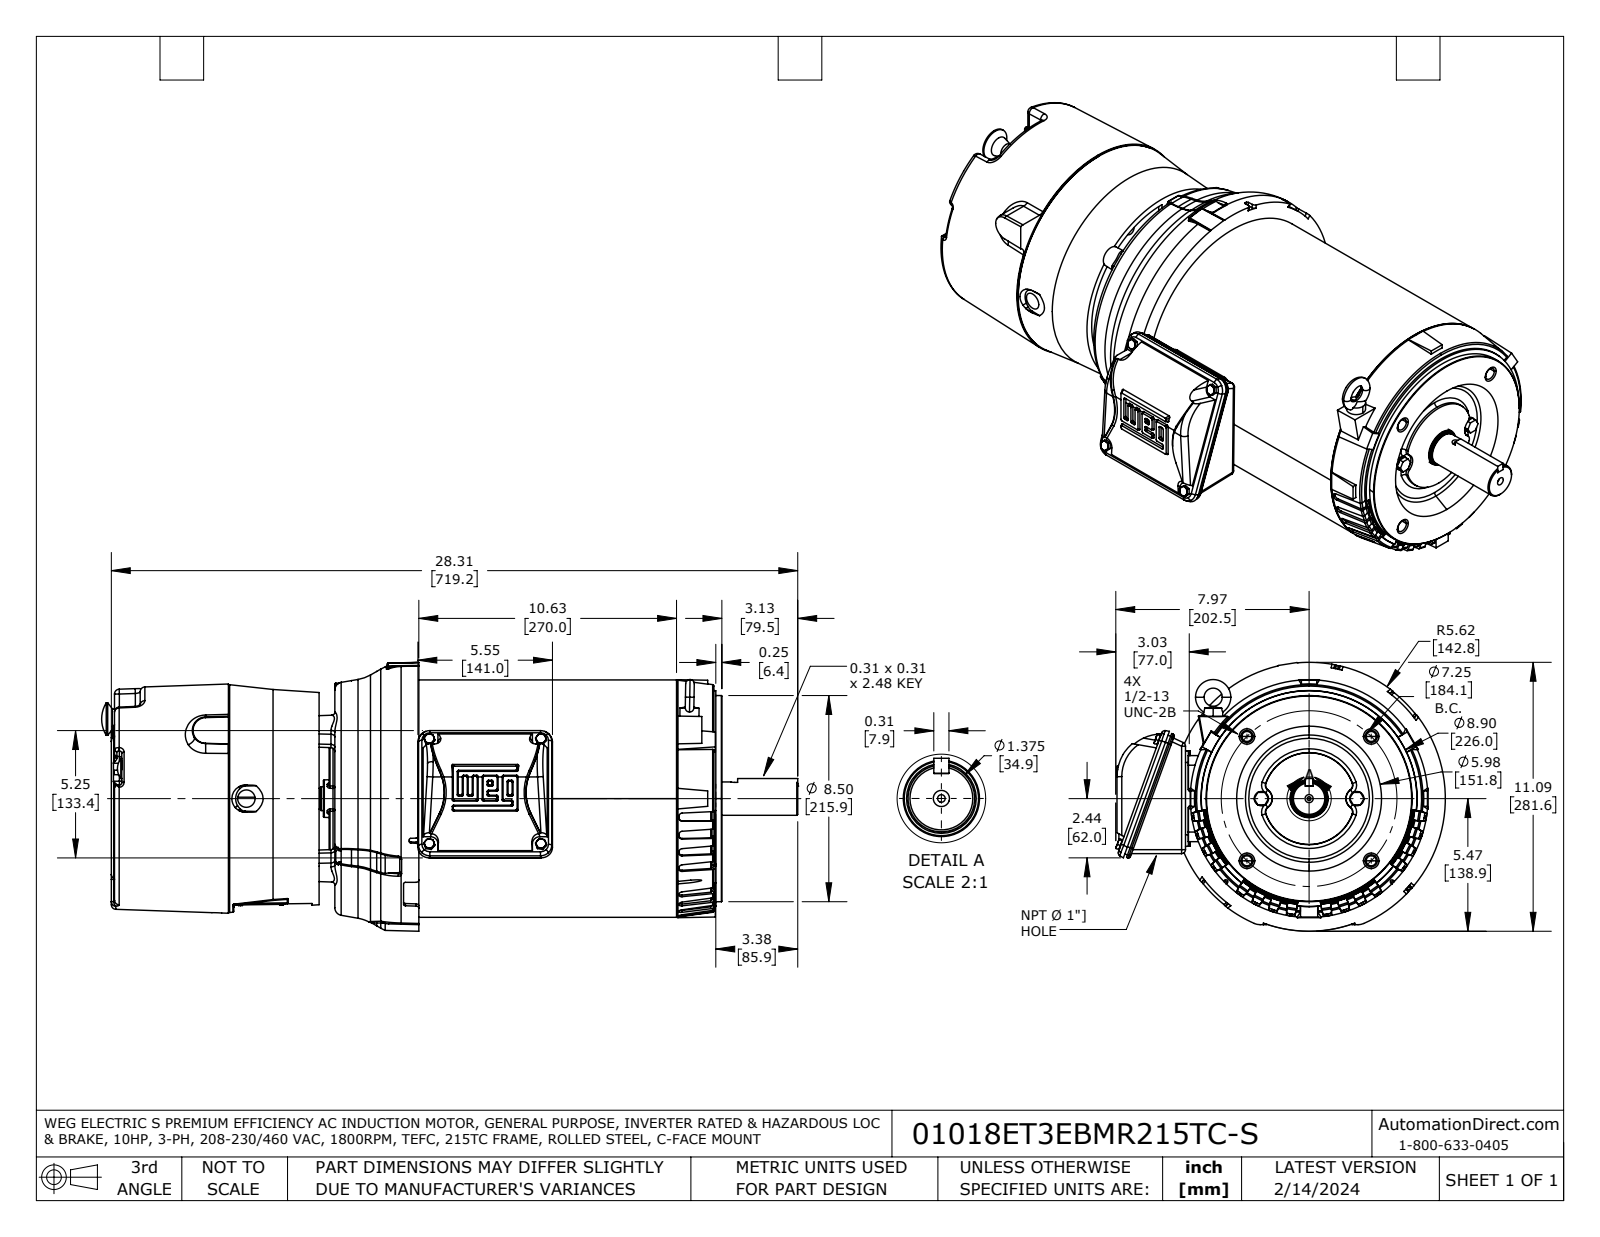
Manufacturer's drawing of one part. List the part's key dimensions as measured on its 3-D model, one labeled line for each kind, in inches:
Part name (STEP PRODUCT): 01018ET3EBMR215TC-S
STEP written by: SolidWorks 2021 (AUTOMOTIVE_DESIGN)
Units: inches
Bodies: 28 solids, 3220 faces (1072 planar, 622 cylindrical, 1526 other)
Overall size (bounding box): 28.71 × 13.593 × 11.088
Volume: 1 519 in³ · Surface area: 2 257 in²
Round holes (diameter × count): ⌀0.257 ×6, ⌀0.5 ×5, ⌀0.101 ×4, ⌀0.146 ×4, ⌀0.413 ×4, ⌀0.422 ×4, ⌀0.201 ×3, ⌀0.53 ×3, ⌀0.566 ×3, ⌀0.844 ×3, ⌀1.03 ×3, ⌀0.315 ×2
Round bosses / shafts (diameter × count): ⌀0.354 ×4, ⌀0.112 ×4, ⌀0.81 ×3, ⌀0.5 ×3, ⌀0.591 ×2, ⌀0.457 ×2, ⌀9.787 ×1, ⌀9.38 ×1
Partial cylindrical surfaces — rounded edges, fillets, slot ends (radius × count): R0.059 ×58, R0.126 ×32, R0.1 ×29, R0.118 ×24, R0.05 ×23, R0.079 ×22, R0.2 ×22, R0.04 ×19
Main face-to-face distances: 10.63, 3.204, 13.834, 9.16, 12.364, 22.994, 0.19, 0.32, 9.48, 12.684
Hole centre spacings: 4, 1.817, 2.213, 2.631, 3.625, 3.997, 5.127, 5.207
